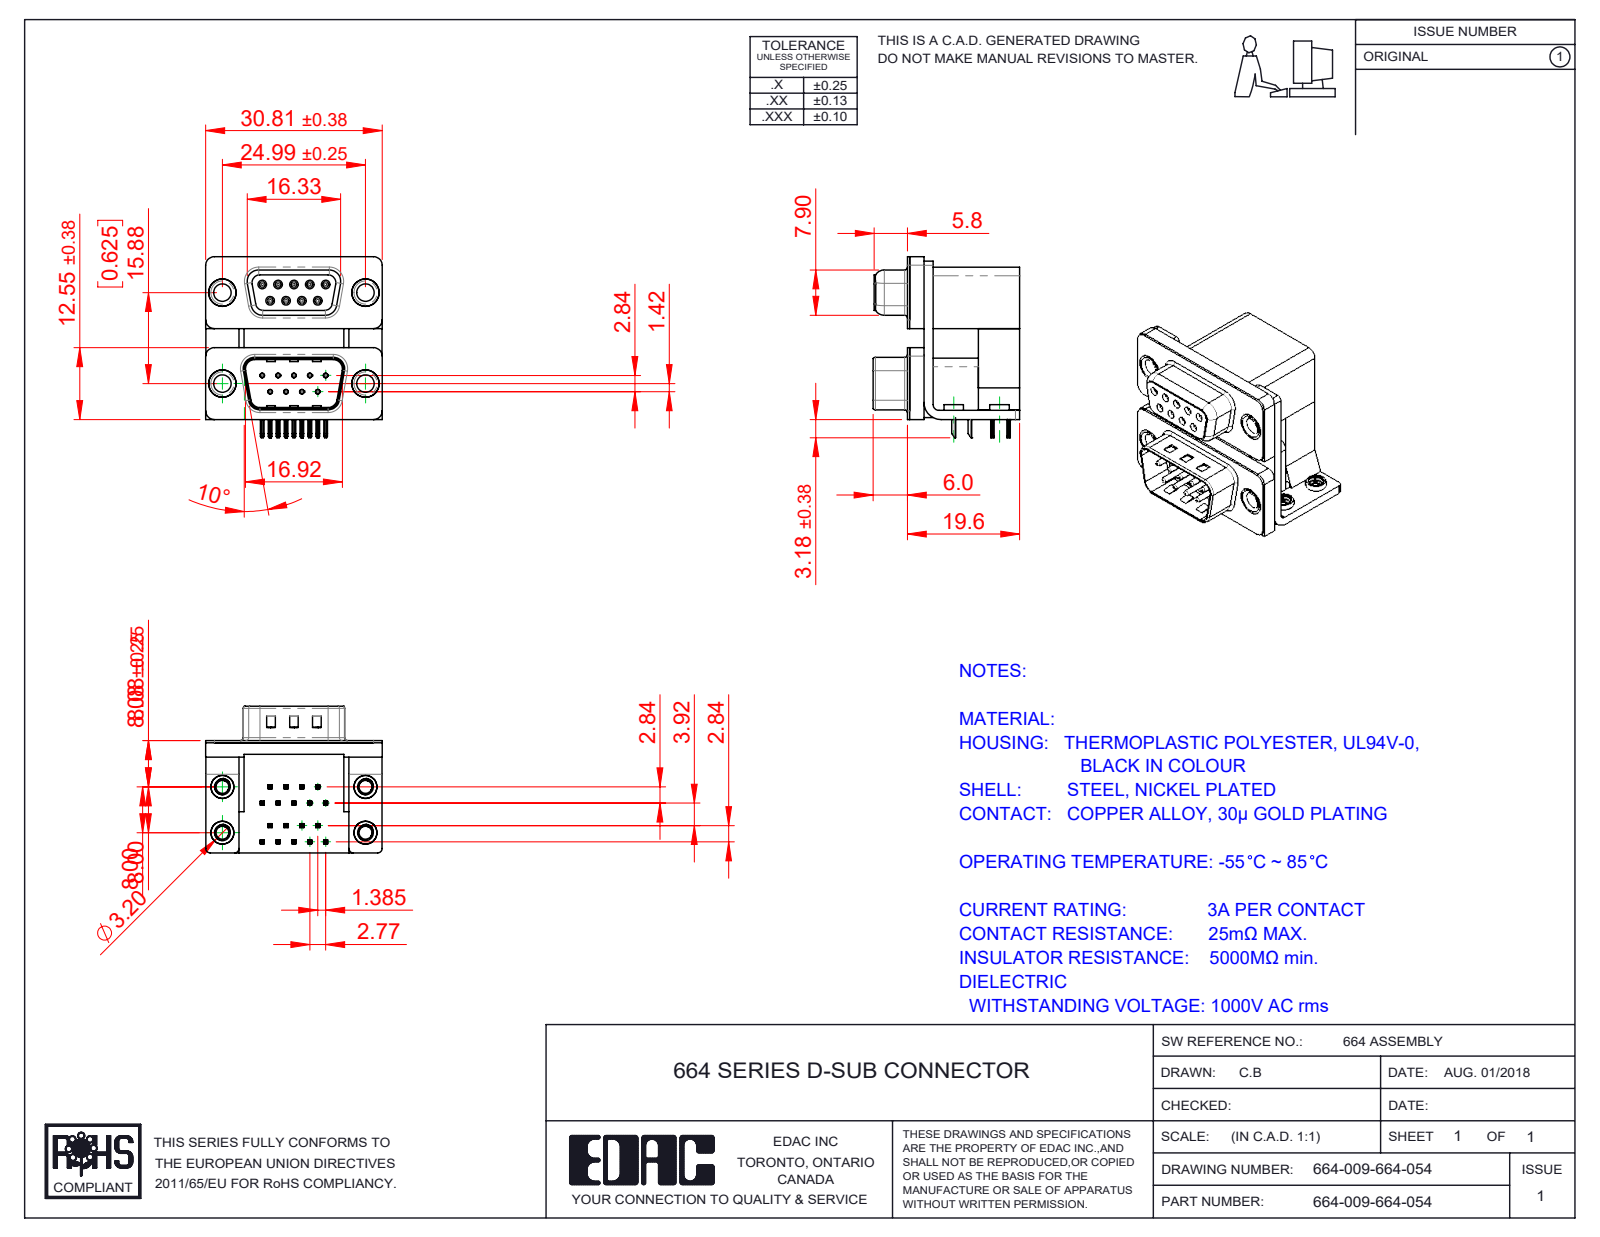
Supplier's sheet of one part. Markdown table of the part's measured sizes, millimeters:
| quantity | value |
| --- | --- |
| part name | 664 Contact Top Upper_L; 664 Contact Top Lower; 664 Shell Receptacle_09 Contacts; 664 Thru Hole Rivet (+8 more) |
| STEP written by | SolidWorks 2020 (CONFIG_CONTROL_DESIGN) |
| units | millimeters |
| bodies | 33 solids, 2585 faces (1275 planar, 735 cylindrical, 575 other) |
| overall size | 31.61 × 30.81 × 25.6 |
| volume | 10 330 mm³ |
| surface area | 12 334 mm² |
| round holes (diameter × count) | 0.8 × 18, 0.35 × 9, 0.9 × 9, 2.26 × 4, 2.75 × 4, 3.05 × 4, 3.2 × 4, 3.5 × 4, 4 × 4, 4.8 × 4, 5 × 4 |
| round bosses / shafts (diameter × count) | 1.2 × 9, 0.75 × 9, 4.9 × 4, 4.75 × 4, 4 × 4, 3.85 × 4, 3.4 × 4 |
| partial cylindrical surfaces (radius × count) | 0.1 × 72, 0.15 × 36, 0.25 × 36, 0.12 × 18, 0.35 × 18, 1.5 × 13, 0.5 × 12, 1.35 × 10 |
| main face-to-face distances | 0.4, 2.5, 16.7, 19.2, 19.6, 2.9, 7.2, 9.5, 12, 12.4 |
| hole center spacings | 3.16, 2.77, 16.12, 15.88, 5.54, 16.82, 13.11, 18.77 |
